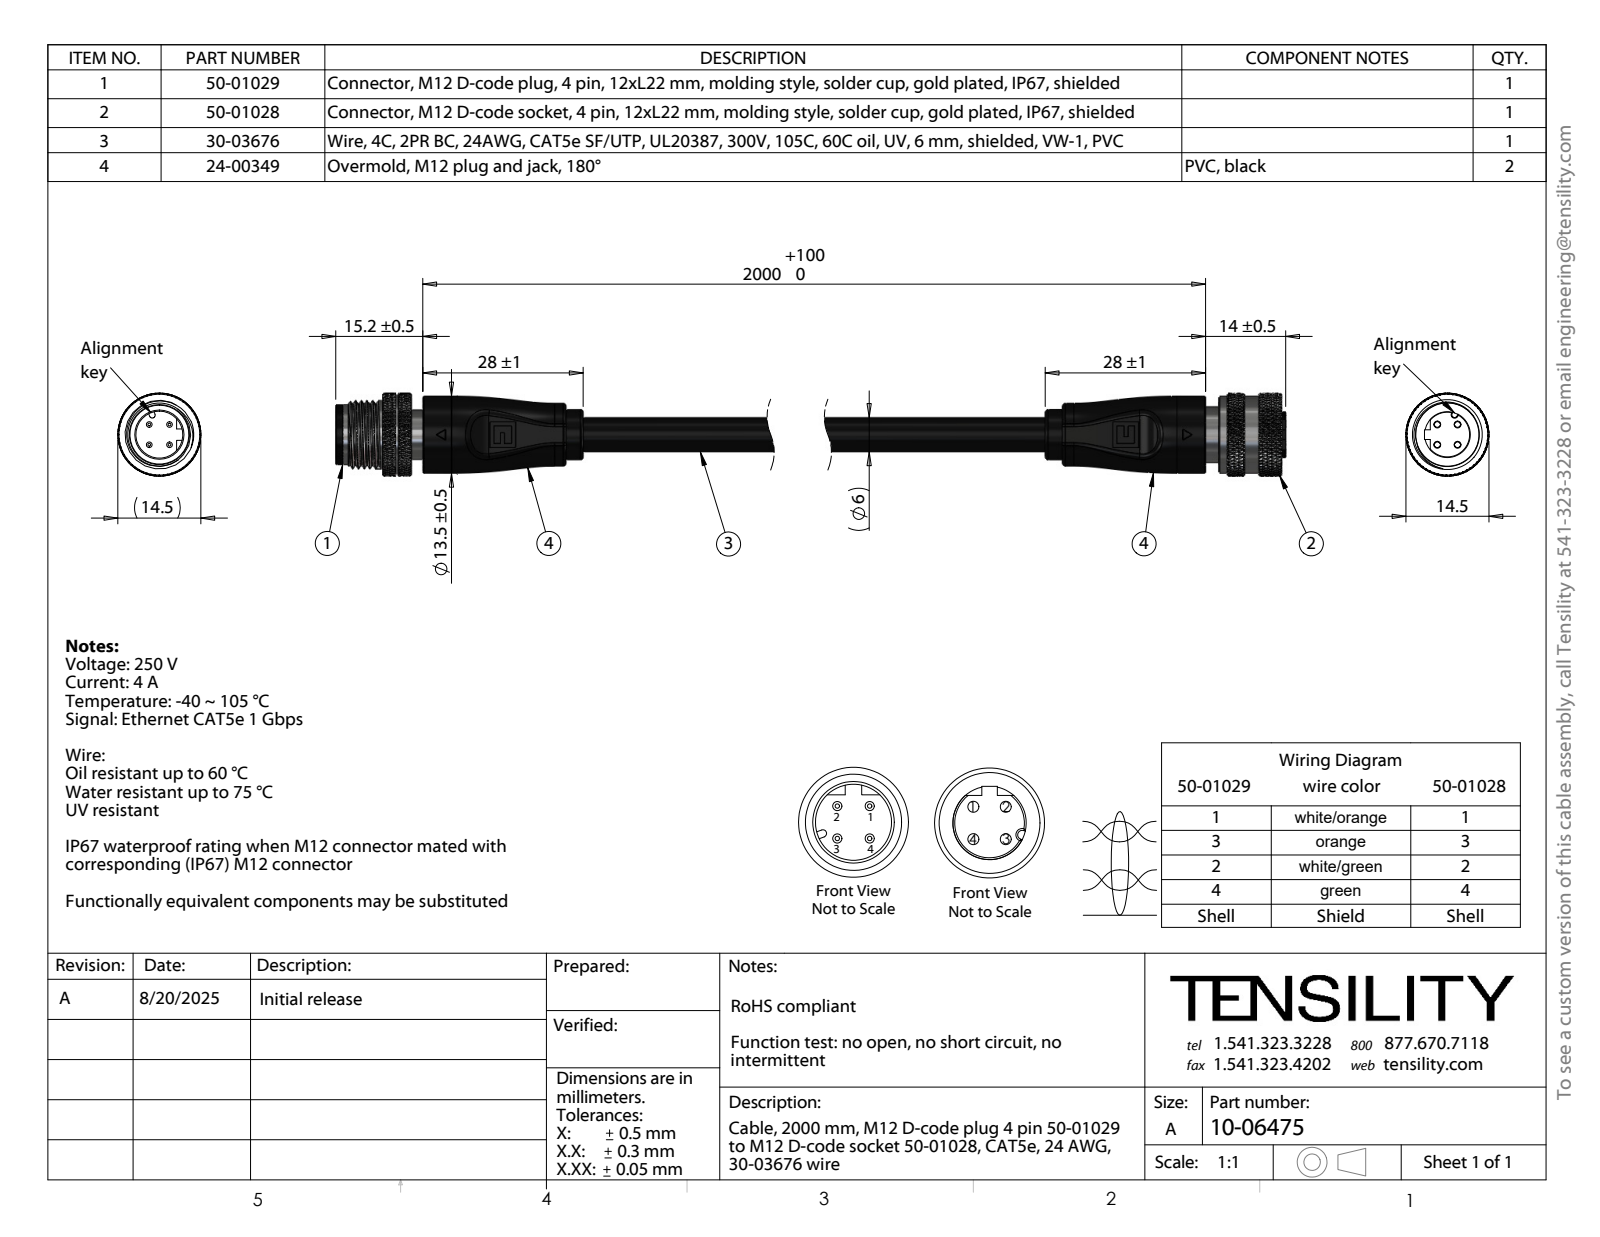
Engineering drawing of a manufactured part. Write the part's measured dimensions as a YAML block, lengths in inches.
part_name: "50-01029-02_默认; 30-03676_blunt cut; 50-01028_默认; 50-01029-04_默认 (+8 more)"
step_written_by: "SolidWorks 2025 (CONFIG_CONTROL_DESIGN)"
units: inches
bodies: {solids: 53, faces: 5792, planar: 362, cylindrical: 1477, other: 3953}
overall_size: [9.26, 0.571, 0.571]
volume: 0.838
surface_area: 47.49
round_holes:
  - {diameter: 0.008, count: 28}
  - {diameter: 0.039, count: 4}
  - {diameter: 0.041, count: 4}
  - {diameter: 0.043, count: 4}
  - {diameter: 0.047, count: 4}
  - {diameter: 0.124, count: 1}
  - {diameter: 0.126, count: 1}
  - {diameter: 0.14, count: 1}
  - {diameter: 0.323, count: 1}
  - {diameter: 0.374, count: 1}
  - {diameter: 0.394, count: 1}
  - {diameter: 0.441, count: 1}
round_bosses_or_shafts:
  - {diameter: 0.063, count: 4}
  - {diameter: 0.059, count: 4}
  - {diameter: 0.055, count: 4}
  - {diameter: 0.571, count: 1}
  - {diameter: 0.547, count: 1}
  - {diameter: 0.531, count: 1}
  - {diameter: 0.472, count: 1}
  - {diameter: 0.433, count: 1}
partial_cylinders:
  - {radius: 0.004, count: 10}
  - {radius: 0.016, count: 6}
  - {radius: 0.02, count: 4}
  - {radius: 0.059, count: 2}
  - {radius: 0.077, count: 2}
  - {radius: 0.197, count: 2}
  - {radius: 0.22, count: 1}
  - {radius: 0.266, count: 1}
face_to_face_distances: [8.11, 0.276, 1.102, 7.008, 0.079, 8.189, 0.15, 8.339, 8.201, 0.228]
hole_center_spacings: [0.075, 0.014, 0.082, 0.042, 0.035, 0.043, 0.049, 0.071]
